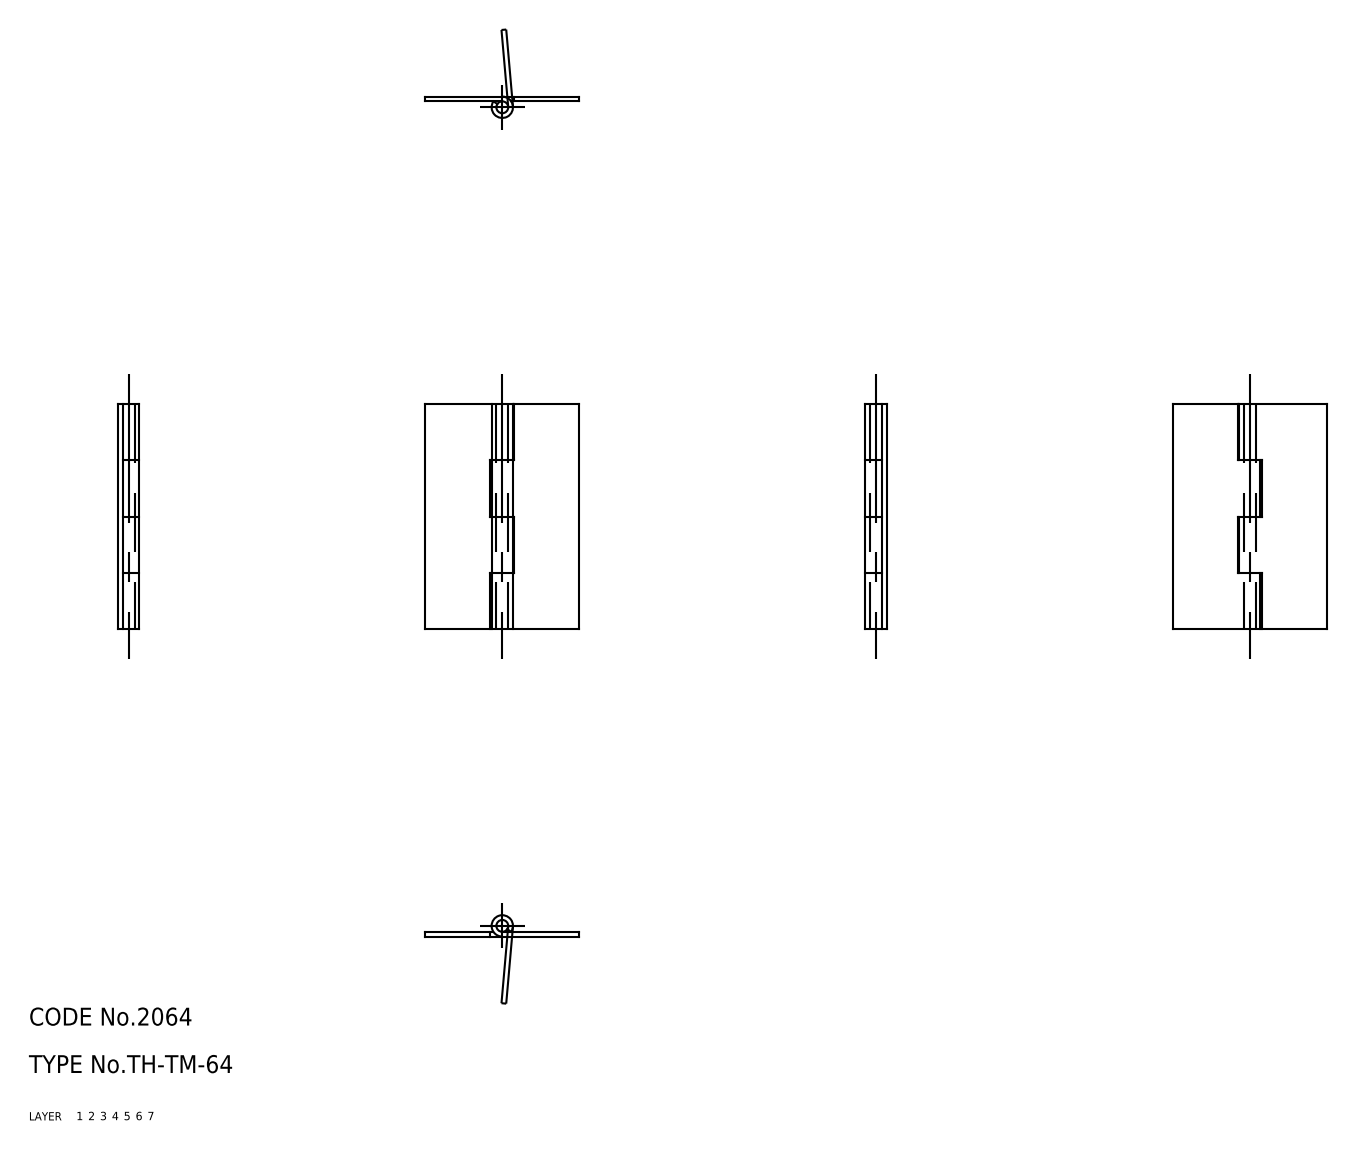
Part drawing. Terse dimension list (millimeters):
name: hinge piece_B; hinge piece_A; shaft; TH_TM_64_24730_36
written by: CADfix (AUTOMOTIVE_DESIGN)
unit: mm
bodies: 3 solids, 36 faces (0 planar, 0 cylindrical, 36 other)
size: 38 × 26 × 3.6
volume: 1 073 mm³; area: 2 847 mm²
